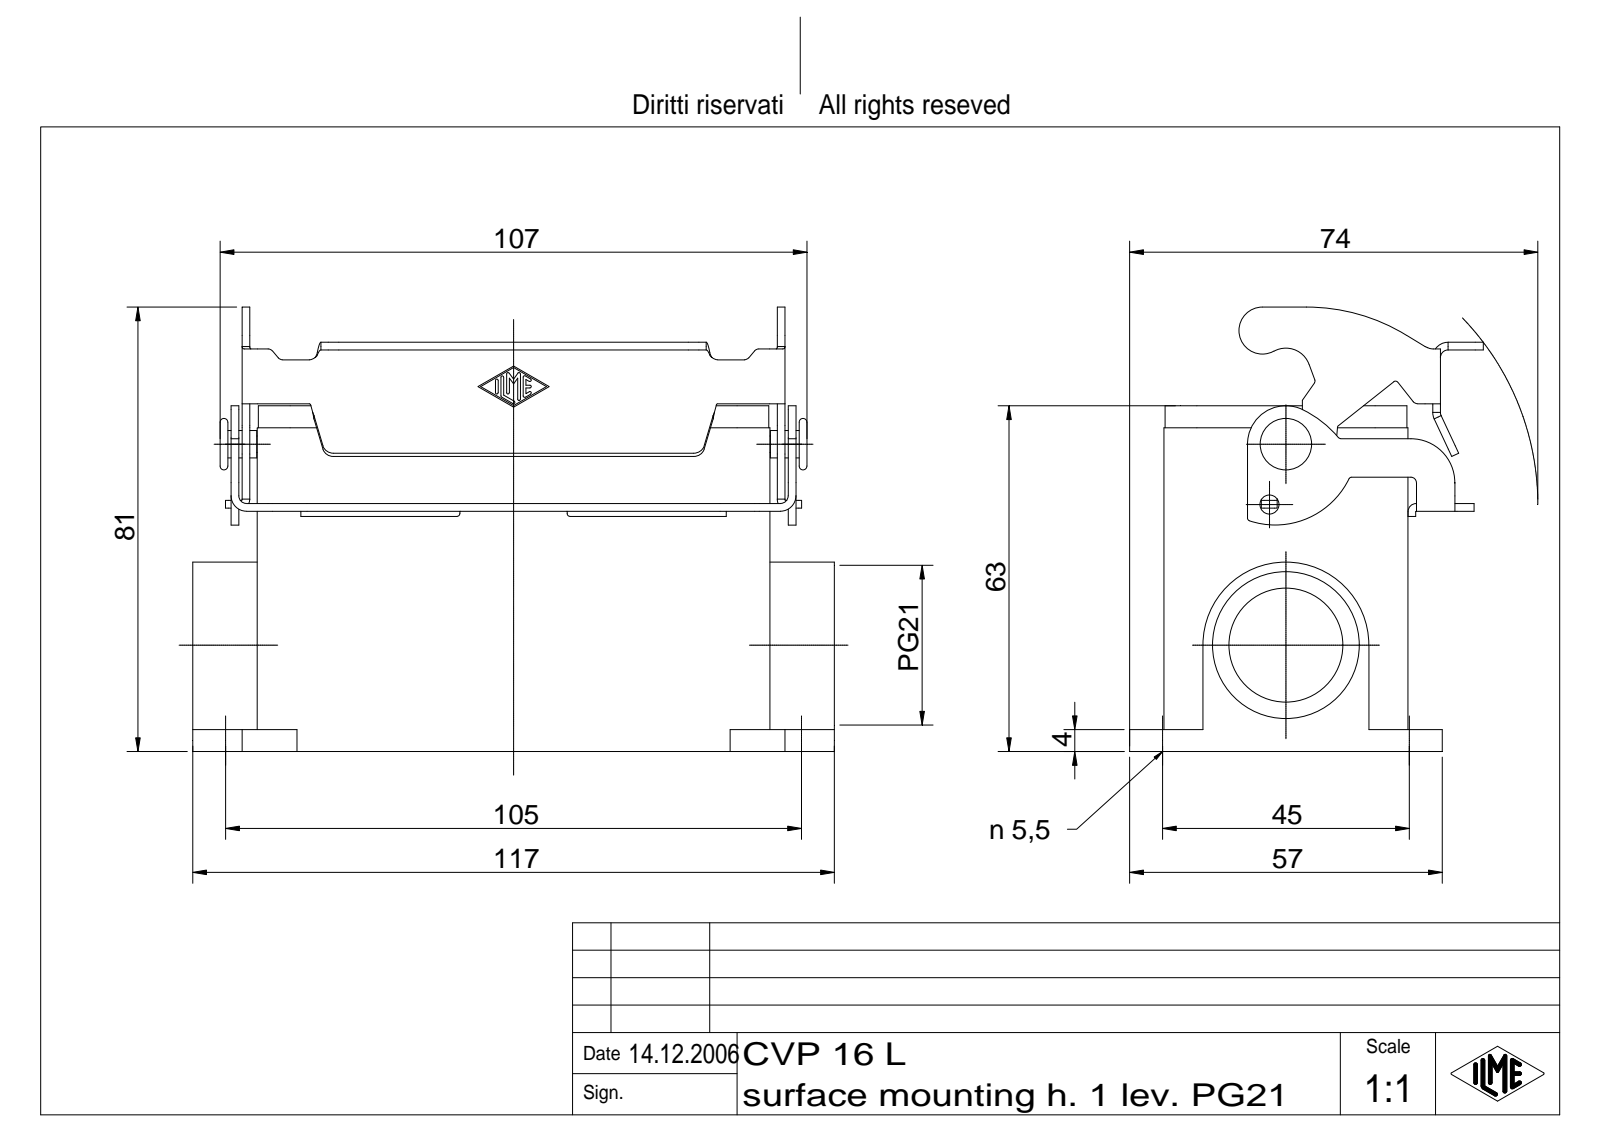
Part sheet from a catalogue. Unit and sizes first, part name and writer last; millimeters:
Units: millimetres
Overall size (bounding box): 117 × 81 × 64.48
Round holes (diameter × count): ⌀5.5 ×4, ⌀3.5 ×1, ⌀20.78 ×1, ⌀26.78 ×1
Round bosses / shafts (diameter × count): ⌀5 ×1, ⌀3.2 ×1, ⌀3 ×1
Partial cylindrical surfaces — rounded edges, fillets, slot ends (radius × count): R0.25 ×15, R0.5 ×9, R1.5 ×9, R1 ×8, R1.4 ×6, R2 ×6, R2.8 ×6, R1.8 ×4
Main face-to-face distances: 4, 40.5, 44.5, 36.5, 1.4, 11.5, 82, 40.3, 4.2, 6.75
Hole centre spacings: 45, 105, 114.24, 25.79
Volume: 108 363 mm³ · Surface area: 58 563 mm²
Bodies: 2 solids, 401 faces (141 planar, 116 cylindrical, 144 other)
Part name (STEP PRODUCT): CVP 16 L
STEP written by: Autodesk Inventor 7 (AUTOMOTIVE_DESIGN)
